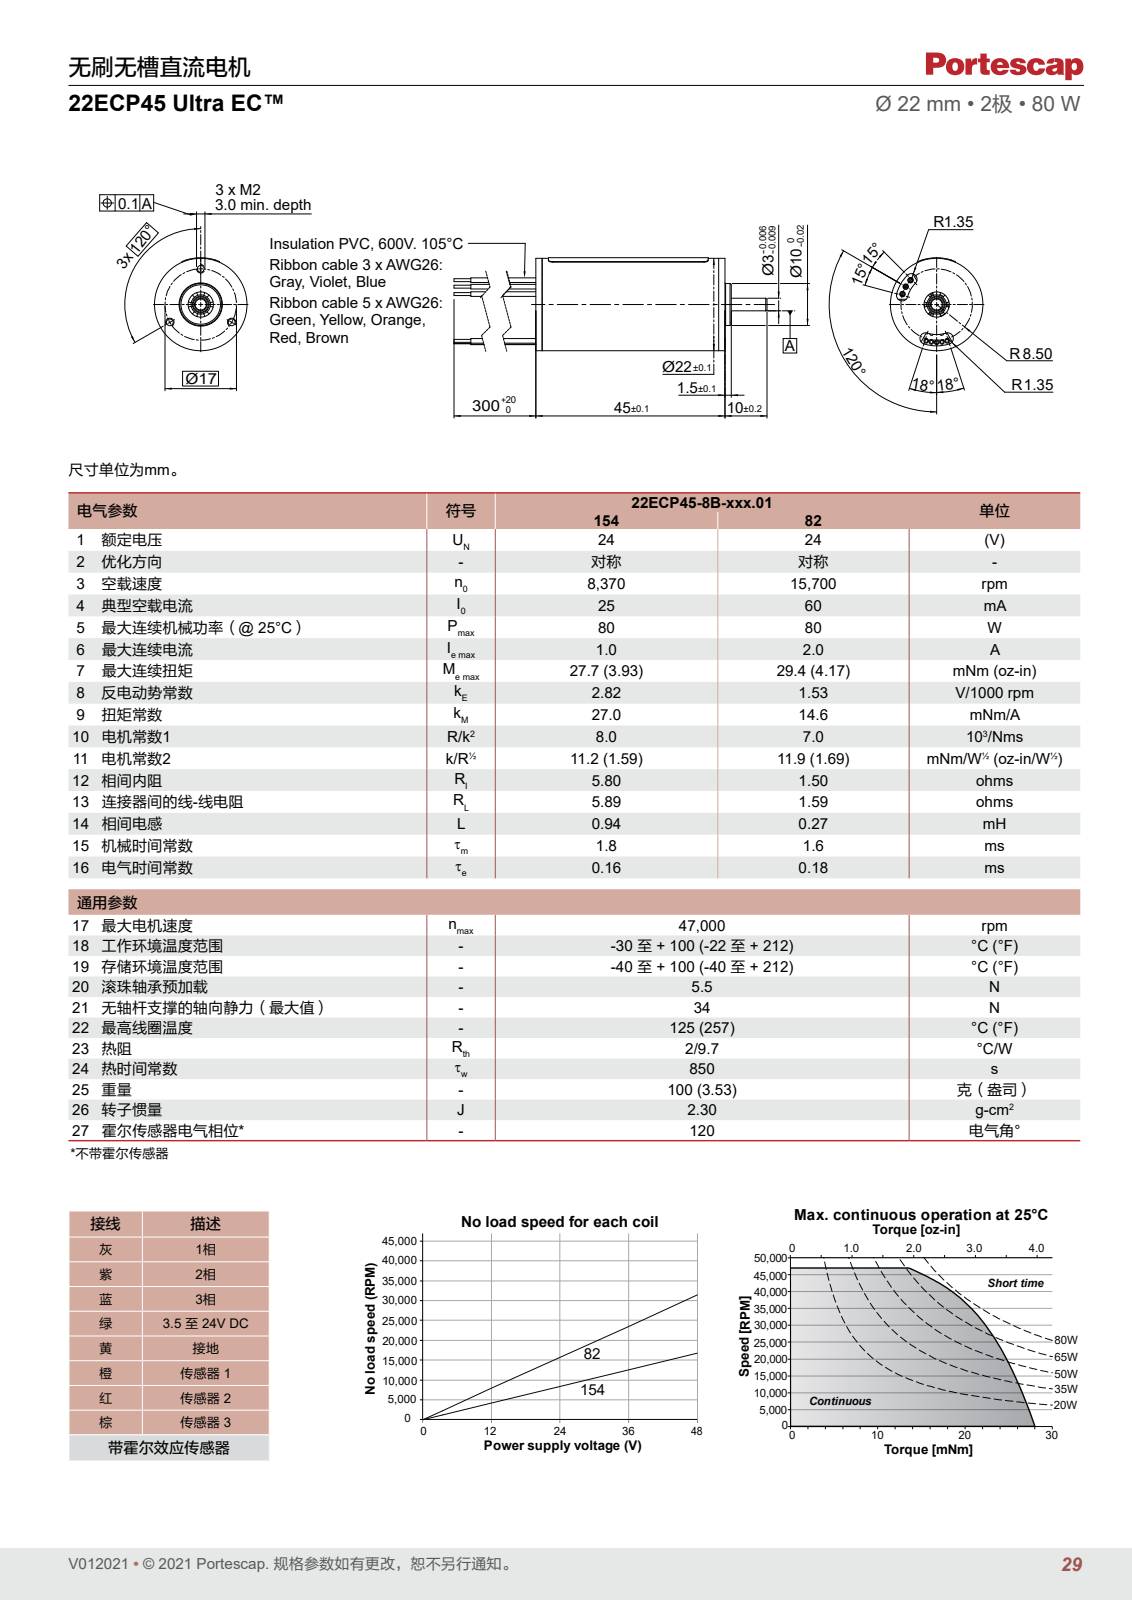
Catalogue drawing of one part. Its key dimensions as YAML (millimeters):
part_name: "22ECP45"
step_written_by: "SolidWorks 2010 (CONFIG_CONTROL_DESIGN)"
units: millimeters
bodies: {solids: 1, faces: 140, planar: 35, cylindrical: 75, other: 30}
overall_size: [357.4, 22.15, 22]
volume: 19453
surface_area: 12718
round_holes:
  - {diameter: 1.6, count: 3}
  - {diameter: 6, count: 1}
  - {diameter: 6.4, count: 1}
  - {diameter: 8, count: 1}
round_bosses_or_shafts:
  - {diameter: 1.1, count: 8}
  - {diameter: 0.7, count: 8}
  - {diameter: 22, count: 1}
  - {diameter: 10, count: 1}
  - {diameter: 4.6, count: 1}
  - {diameter: 3, count: 1}
partial_cylinders:
  - {radius: 1, count: 4}
  - {radius: 1.35, count: 4}
  - {radius: 7.15, count: 1}
  - {radius: 9.85, count: 1}
  - {radius: 11.15, count: 1}
face_to_face_distances: [45, 1.99, 43.01, 1, 46.5, 44.51, 1.5, 0.99, 44, 45.5]
hole_center_spacings: [8.5, 14.72]
